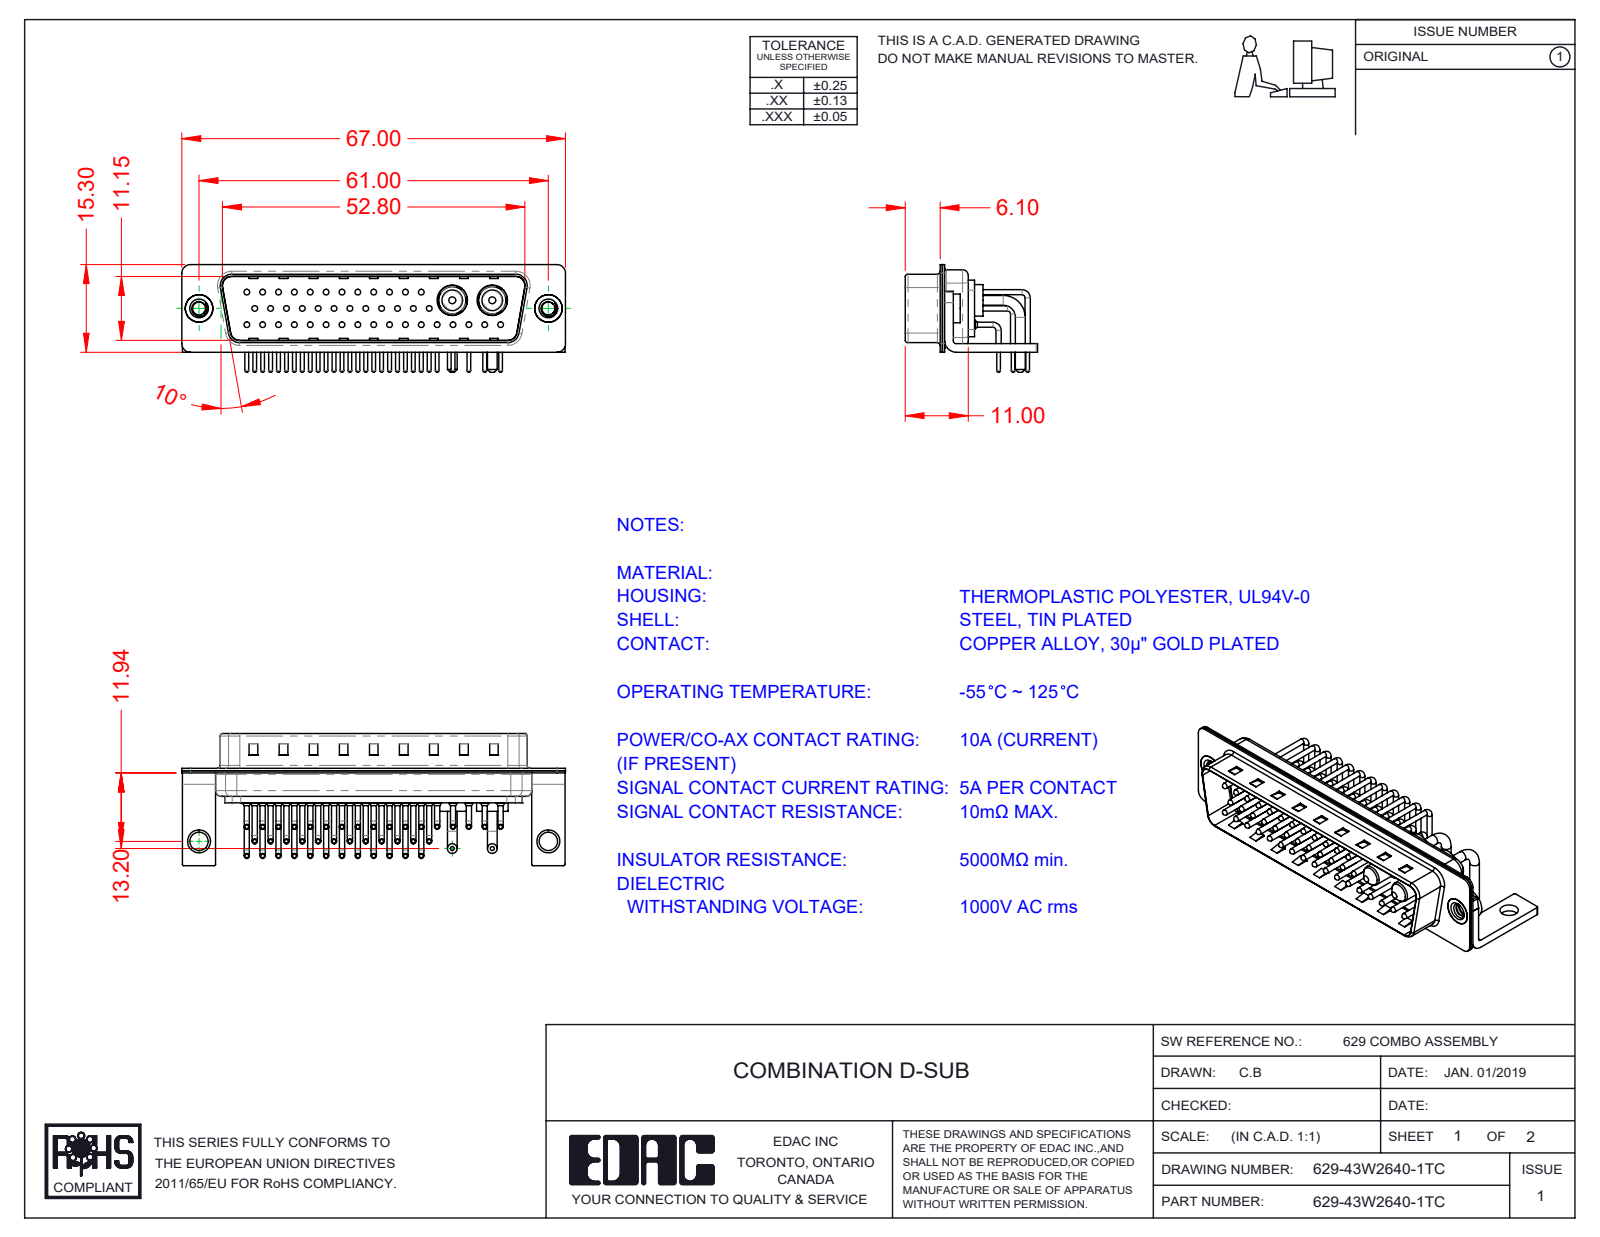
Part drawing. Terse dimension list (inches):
name: 629Combo Housing_43W2; 629-43W2640-1TC; 629Combo Shell Rear_50 Contacts; 629Combo Stabilizer Bracket_50 Contacts (+6 more)
written by: SolidWorks 2020 (CONFIG_CONTROL_DESIGN)
unit: in
bodies: 52 solids, 5056 faces (2867 planar, 1683 cylindrical, 506 other)
size: 2.638 × 0.909 × 0.74
volume: 0.333 in³; area: 20.5 in²
holes: 41× ⌀0.03, 41× ⌀0.063, 41× ⌀0.079, 2× ⌀0.089, 2× ⌀0.126, 2× ⌀0.157, 2× ⌀0.189, 2× ⌀0.191, 2× ⌀0.209
bosses: 82× ⌀0.035, 41× ⌀0.059, 41× ⌀0.039, 41× ⌀0.026, 4× ⌀0.067, 2× ⌀0.217, 2× ⌀0.205, 2× ⌀0.197
rounds: 41× R0.04, 16× R0.01, 16× R0.059, 13× R0.079, 9× R0.02, 8× R0.063, 4× R0.024, 4× R0.026
face distances: 0.016, 0.059, 0.455, 0.22, 0.205, 0.031, 0.161, 0.236, 0.031, 0.075
hole spacings: 0.109, 0.218, 0.124, 0.327, 0.436, 0.545, 0.654, 0.763
